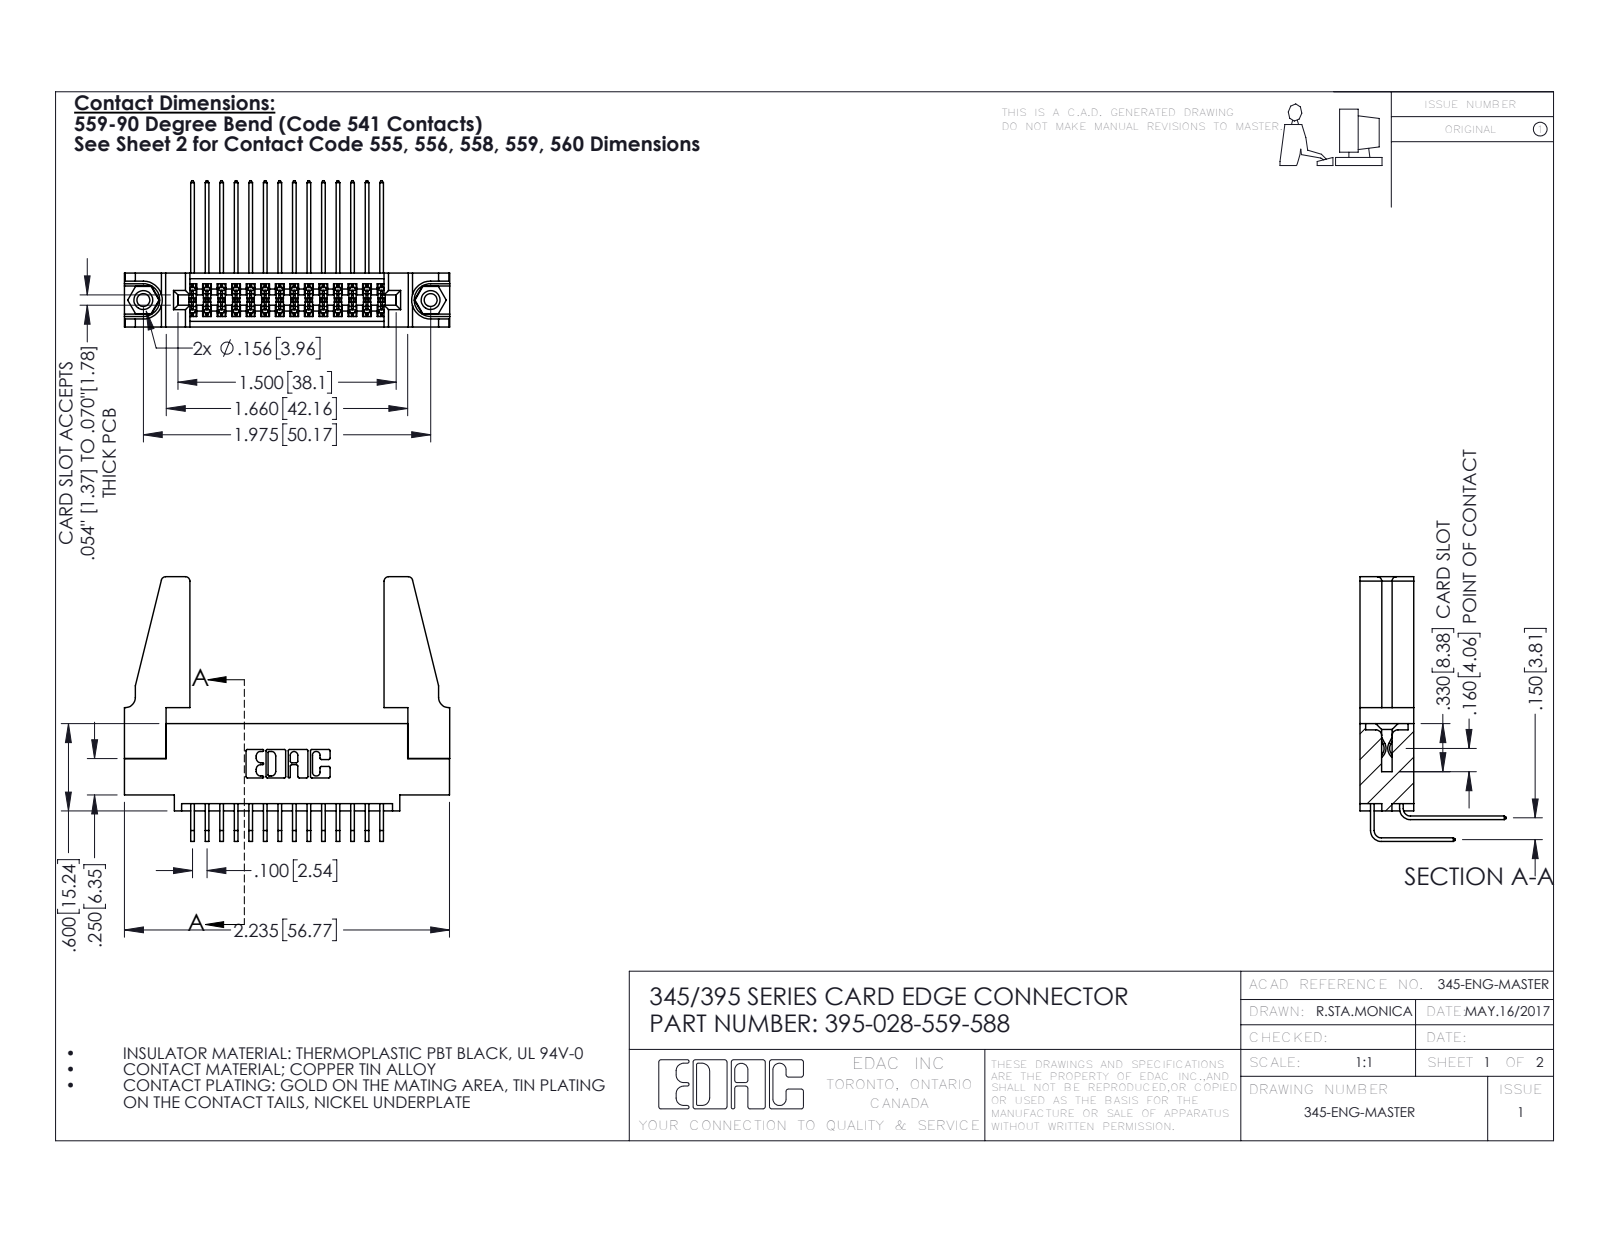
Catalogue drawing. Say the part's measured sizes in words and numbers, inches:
The part is named "345 Part_0.110 Offset - 0.156 Dia-TH; 395-028-559-588; 345-292-001_558 559 Tail - 1; 345-220-078_345-220-088 (+2 more)". Its 3-D file was written by "SolidWorks 2016 (CONFIG_CONTROL_DESIGN)". It is 33 solids with 1710 faces: 1136 planar, 558 cylindrical and 16 other. Overall it measures 2.236 by 1.819 by 1.005 inches. Its volume is 0.525 cubic inches and its surface area 17.57 square inches. Round holes: 2 of diameter 0.089, 2 of diameter 0.125, 2 of diameter 0.156, 1 of diameter 0.064. Round bosses or shafts: 2 of diameter 0.155. Partial cylindrical surfaces (rounded edges, fillets, slot ends): 42 of radius 0.006, 22 of radius 0.01, 8 of radius 0.03, 6 of radius 0.007, 6 of radius 0.031, 3 of radius 0.026, 2 of radius 0.014, 2 of radius 0.019. The main face-to-face distances are 0.37, 0.072, 0.298, 0.2, 0.098, 0.272, 0.025, 0.225, 0.15, 0.175. The hole center spacings are 0.27, 1.742, 1.975.
